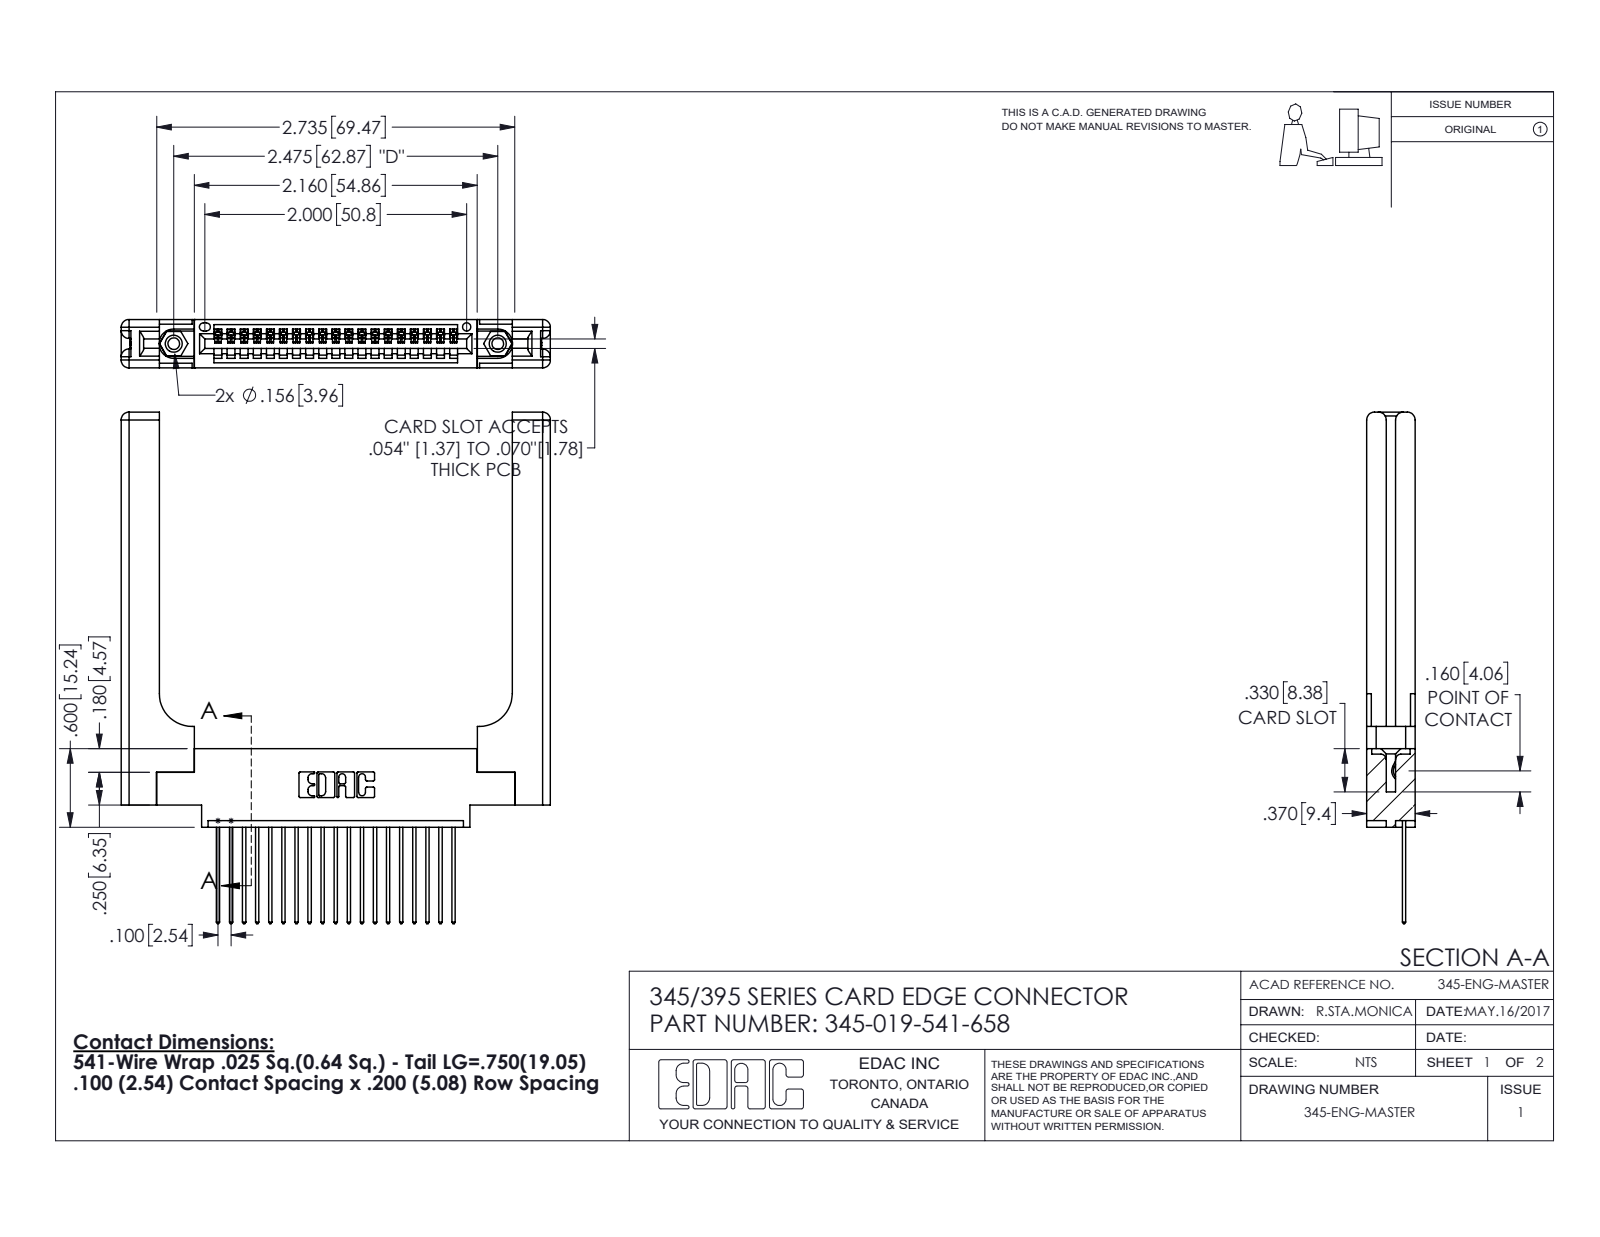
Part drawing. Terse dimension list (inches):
name: 345 Part_0.170 Offset - 0.156 Dia-TH; 345-292-001_345-293-141; 345-019-541-658; 345-250-001_345-250-001-102 (+1 more)
written by: SolidWorks 2016 (CONFIG_CONTROL_DESIGN)
unit: in
bodies: 24 solids, 1488 faces (992 planar, 436 cylindrical, 60 other)
size: 3.907 × 3.279 × 0.37
volume: 0.987 in³; area: 24.31 in²
holes: 2× ⌀0.089, 2× ⌀0.125, 2× ⌀0.156, 1× ⌀0.064
bosses: 2× ⌀0.155
rounds: 38× R0.006, 38× R0.01, 22× R0.01, 16× R0.06, 6× R0.007, 6× R0.031, 3× R0.026, 2× R0.03
face distances: 0.37, 0.072, 0.298, 0.15, 0.148, 0.077, 0.098, 0.272, 0.025, 0.22
hole spacings: 0.27, 2.241, 2.475
